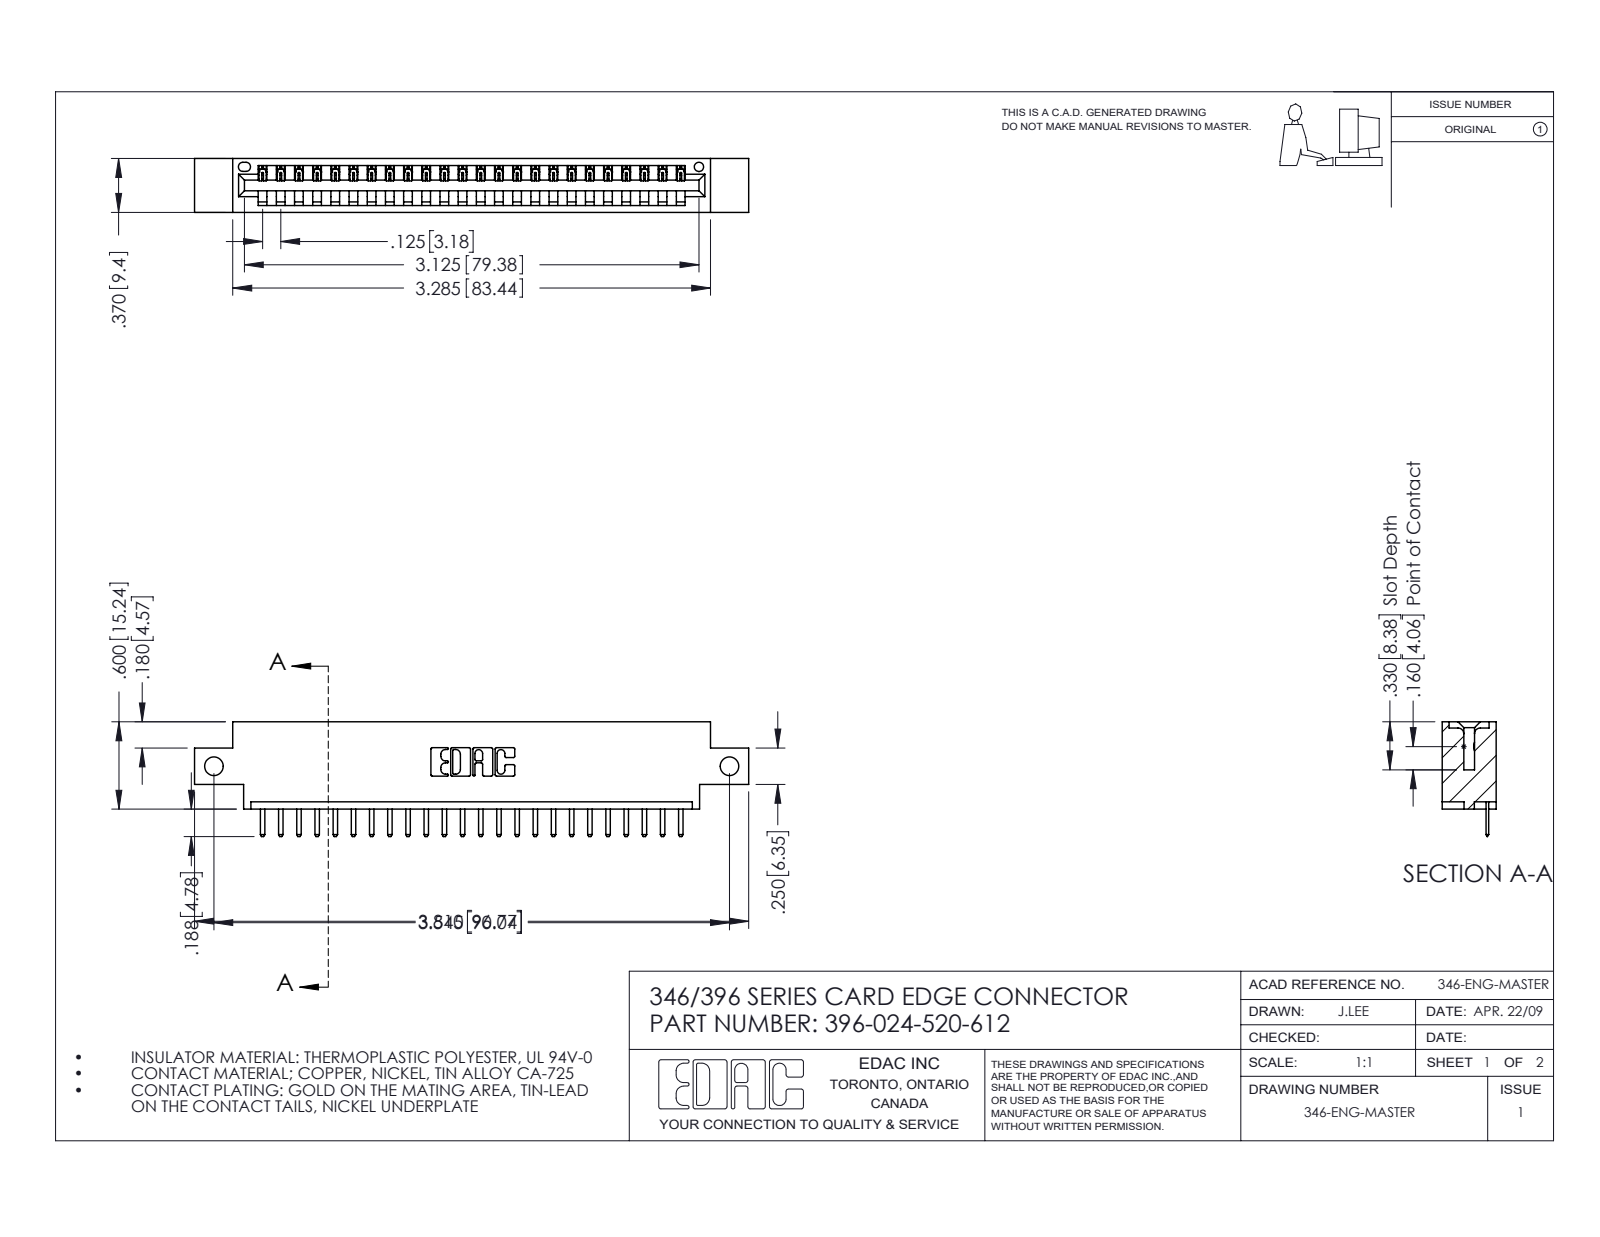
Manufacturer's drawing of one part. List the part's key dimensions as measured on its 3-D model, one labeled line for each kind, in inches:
Part name (STEP PRODUCT): 345-292-001_345-293-120; 396-024-520-612; 346 Part_0.170 Offset - Side Mount
STEP written by: SolidWorks 2016 (CONFIG_CONTROL_DESIGN)
Units: inches
Bodies: 25 solids, 1614 faces (1088 planar, 526 cylindrical, 0 other)
Overall size (bounding box): 3.81 × 0.788 × 0.37
Volume: 0.539 in³ · Surface area: 16.47 in²
Round holes (diameter × count): ⌀0.128 ×2, ⌀0.064 ×1
Partial cylindrical surfaces — rounded edges, fillets, slot ends (radius × count): R0.01 ×50, R0.006 ×48, R0.01 ×22, R0.007 ×6, R0.031 ×6, R0.026 ×3, R0.031 ×2, R0.04 ×2
Main face-to-face distances: 0.37, 0.048, 0.322, 0.25, 0.148, 0.222, 0.1, 0.174, 0.072, 0.298
Hole centre spacings: 3.545
